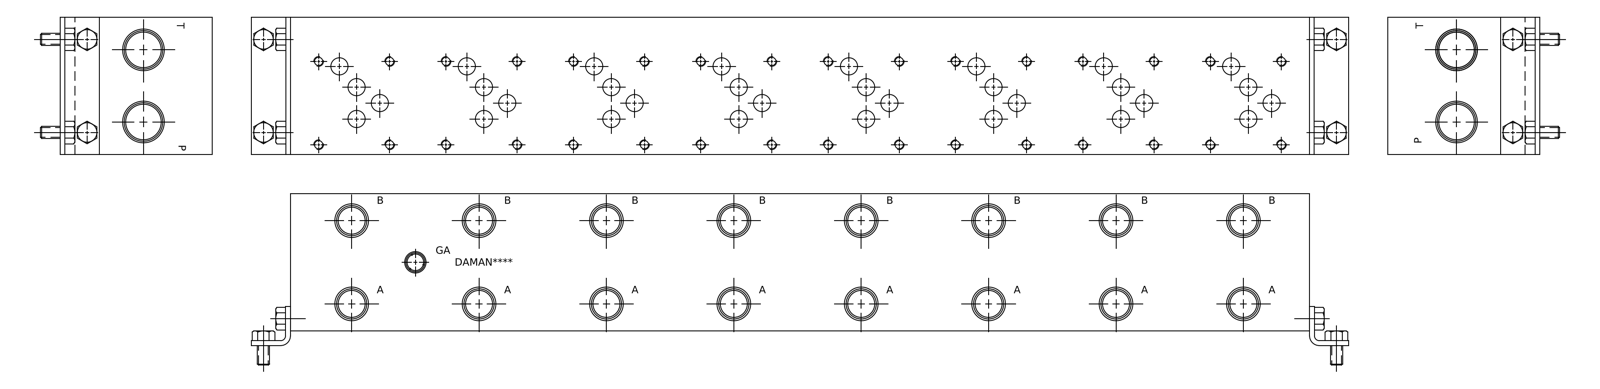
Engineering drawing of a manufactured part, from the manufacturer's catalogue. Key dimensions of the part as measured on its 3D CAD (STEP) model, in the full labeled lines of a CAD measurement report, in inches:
Part name (STEP PRODUCT): Part_AD05P083P_3D
STEP written by: Autodesk Inventor 2020 (AUTOMOTIVE_DESIGN)
Units: inches
Bodies: 1 solid, 1022 faces (538 planar, 146 cylindrical, 338 other)
Overall size (bounding box): 26 × 3.5 × 3.5
Volume: 307.5 in³ · Surface area: 457.2 in²
Round holes (diameter × count): ⌀0.201 ×32, ⌀0.25 ×32, ⌀0.438 ×32, ⌀0.688 ×16, ⌀0.85 ×16, ⌀0.257 ×2, ⌀0.312 ×2, ⌀0.906 ×2, ⌀1.06 ×2, ⌀0.422 ×1, ⌀0.546 ×1
Main face-to-face distances: 3.5, 26, 0.605, 2.895, 0.624, 25.376, 2.75, 0.75, 0.604, 3.498
Hole centre spacings: 3.25, 6.5, 9.75, 9.979, 3.883, 6.839, 13, 13.172
